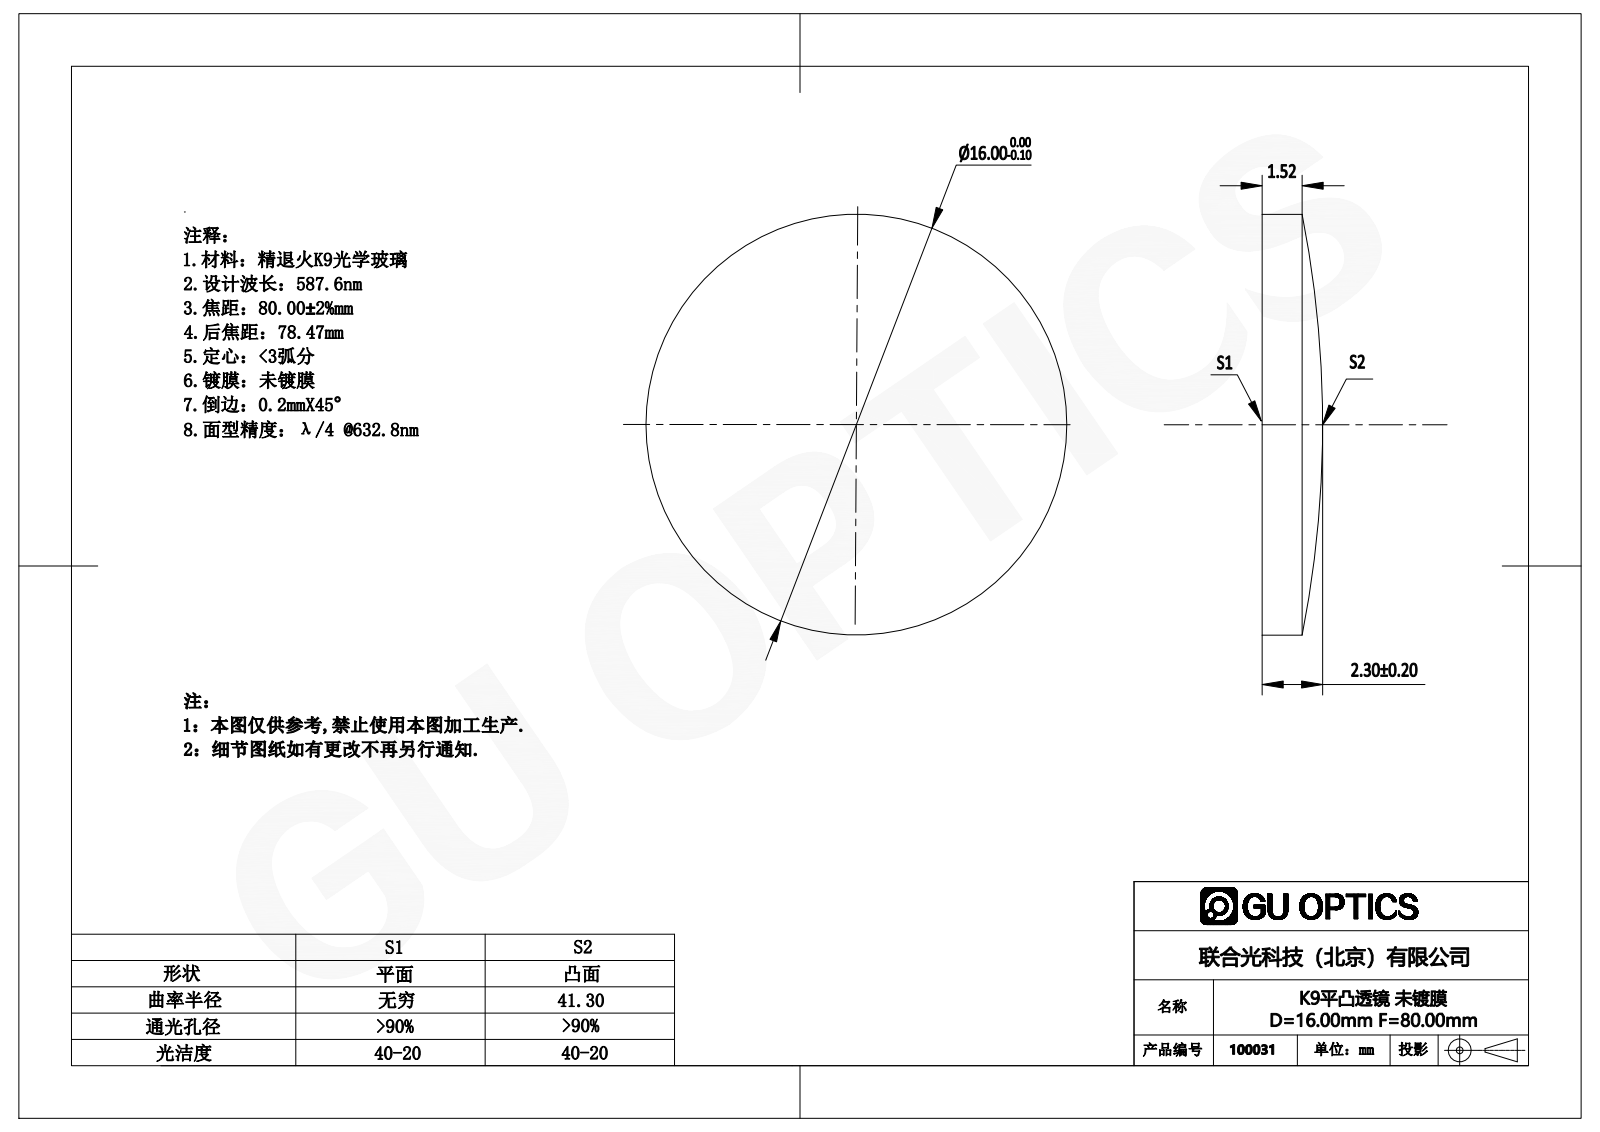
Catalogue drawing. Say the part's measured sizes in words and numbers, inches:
The part is named "100031". Its 3-D file was written by "SolidWorks 2016 (AUTOMOTIVE_DESIGN)". It is 1 solid with 5 faces: 1 planar, 2 cylindrical and 2 other. Overall it measures 0.63 by 0.63 by 0.091 inches. Its volume is 0.023 cubic inches and its surface area 0.744 square inches. Round bosses or shafts: 1 of diameter 0.63.
